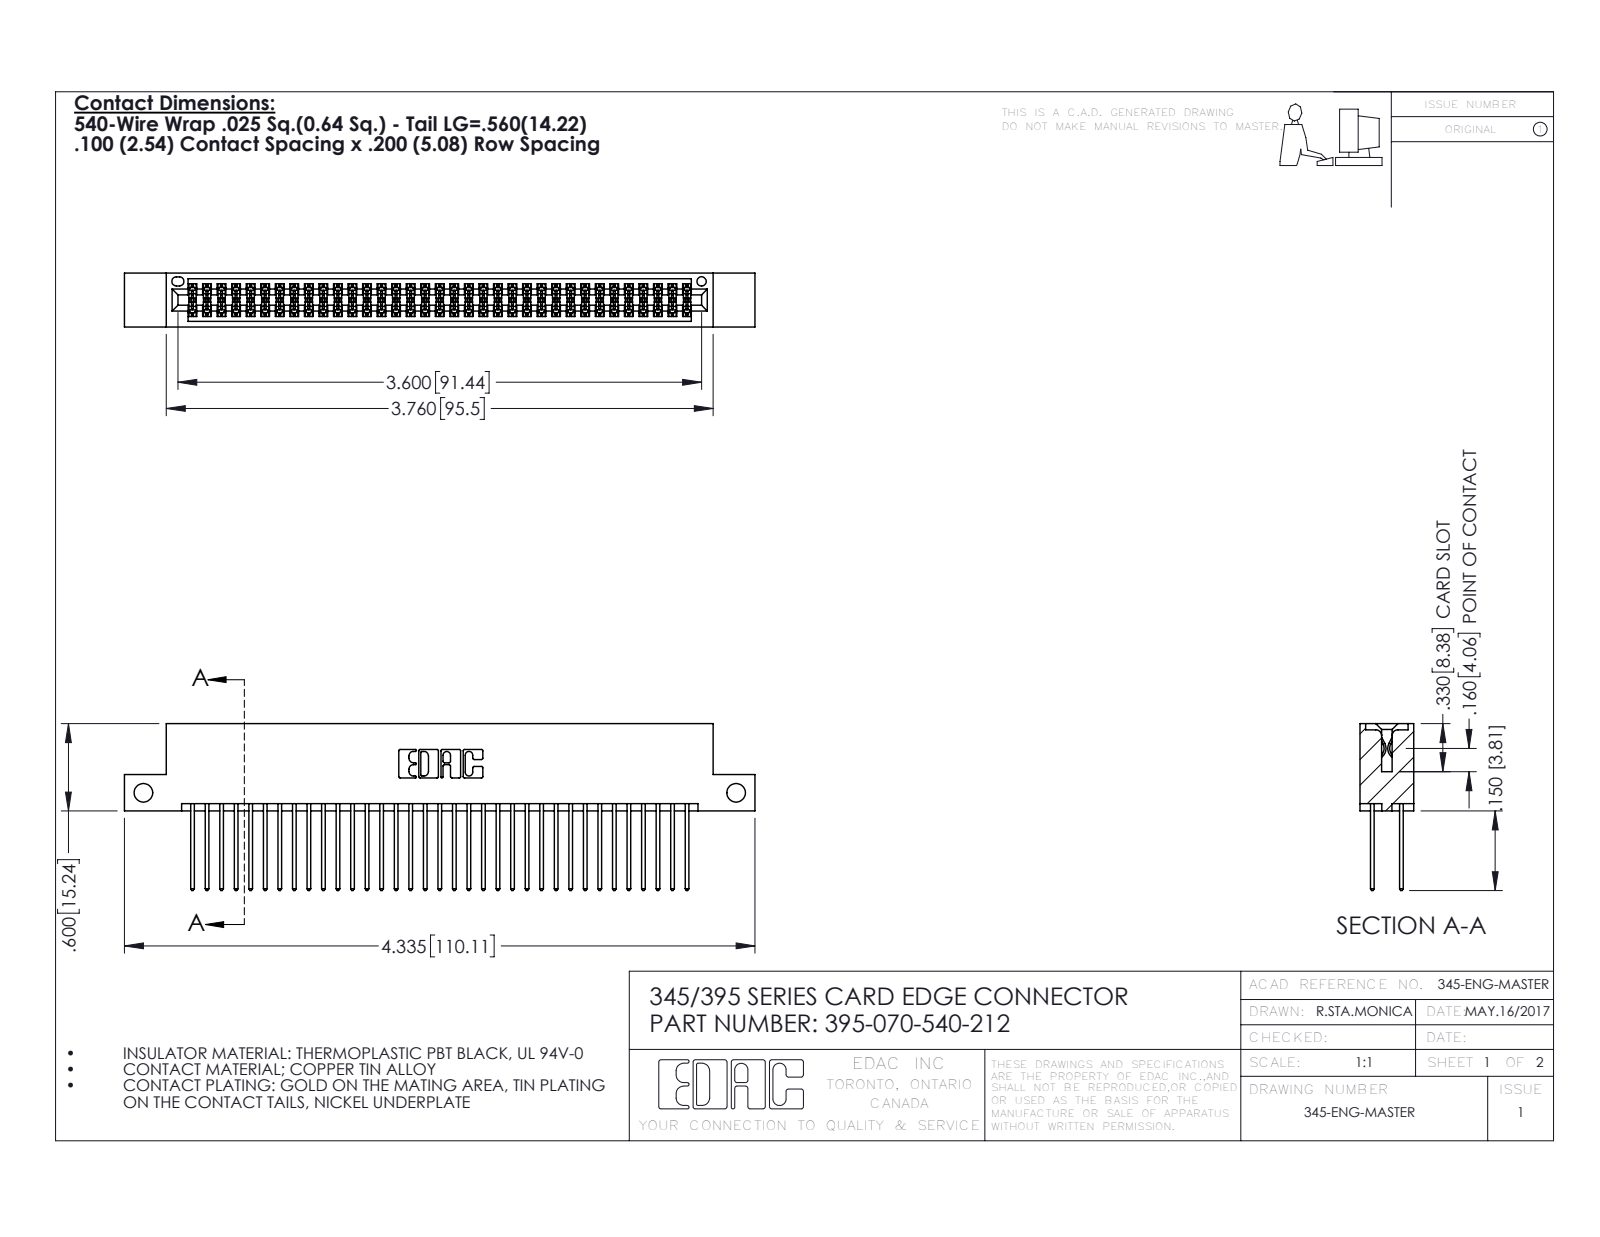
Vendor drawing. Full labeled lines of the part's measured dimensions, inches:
Part name (STEP PRODUCT): 345 Part_Flush Mounting Lugs - Side Mount; 345-292-001_345-293-140; 395-070-540-212
STEP written by: SolidWorks 2016 (CONFIG_CONTROL_DESIGN)
Units: inches
Bodies: 71 solids, 3626 faces (2390 planar, 1236 cylindrical, 0 other)
Overall size (bounding box): 4.335 × 1.147 × 0.37
Volume: 0.66 in³ · Surface area: 26.25 in²
Round holes (diameter × count): ⌀0.128 ×2, ⌀0.064 ×1
Partial cylindrical surfaces — rounded edges, fillets, slot ends (radius × count): R0.006 ×105, R0.01 ×70, R0.01 ×22, R0.007 ×6, R0.031 ×6, R0.026 ×3, R0.014 ×2, R0.019 ×2
Main face-to-face distances: 0.298, 0.072, 0.2, 0.098, 0.272, 0.025, 0.37, 0.225, 0.175, 0.149
Hole centre spacings: 4.075
